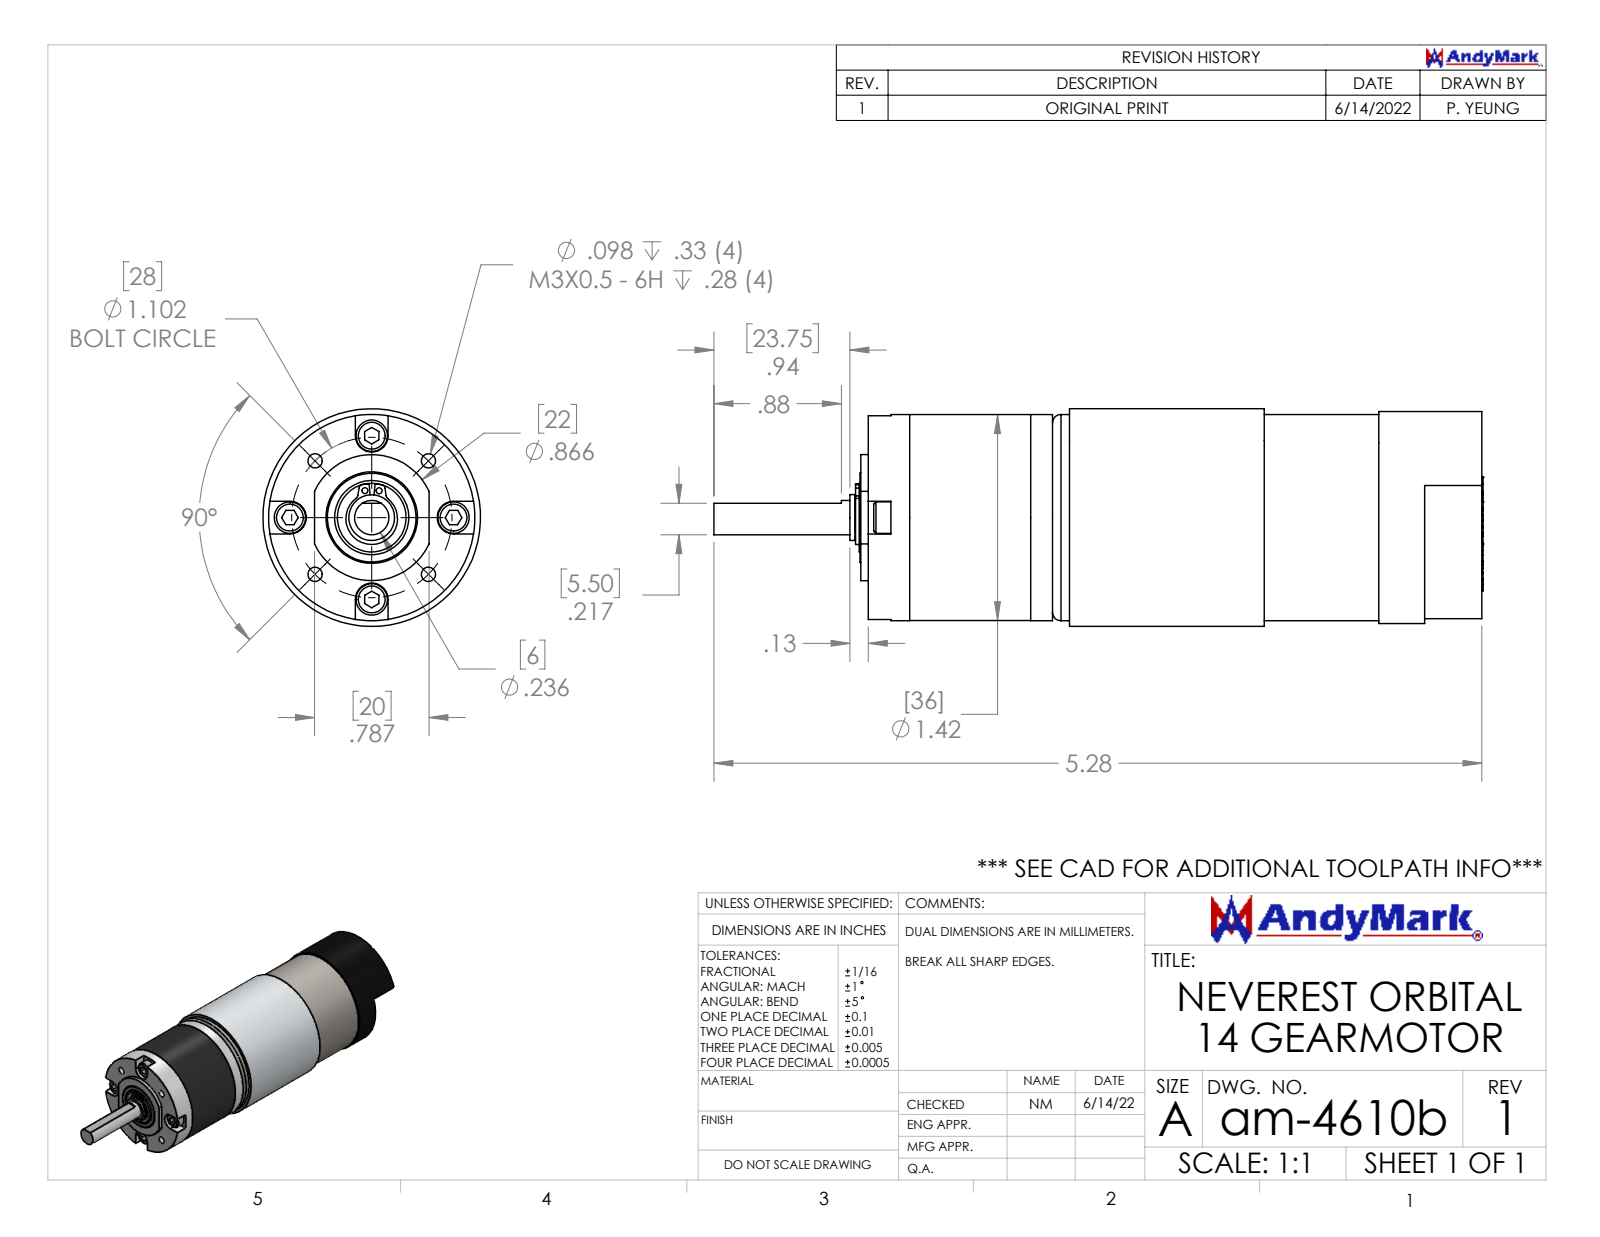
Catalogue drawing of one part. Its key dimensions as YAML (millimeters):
part_name: "am-4610b NeveRest Orbital 14 Gearmotor; am-3104 NeveRest Motor; am-4376 17T 0.5mod NeveRest Orbital Pinion; NR Orbital 2 Stage Gearbox (+5 more)"
step_written_by: "SolidWorks 2021 (AUTOMOTIVE_DESIGN)"
units: millimeters
bodies: {solids: 25, faces: 679, planar: 270, cylindrical: 199, other: 210}
overall_size: [134.3, 38, 38]
volume: 111100
surface_area: 23170
round_holes:
  - {diameter: 2.5, count: 10}
  - {diameter: 3.2, count: 4}
  - {diameter: 3.2, count: 3}
  - {diameter: 1, count: 2}
  - {diameter: 7.4, count: 1}
  - {diameter: 8, count: 1}
  - {diameter: 11, count: 1}
  - {diameter: 13, count: 1}
  - {diameter: 13, count: 1}
  - {diameter: 16, count: 1}
round_bosses_or_shafts:
  - {diameter: 5.5, count: 4}
  - {diameter: 3, count: 4}
  - {diameter: 38, count: 1}
  - {diameter: 37, count: 1}
  - {diameter: 36, count: 1}
  - {diameter: 35.9, count: 1}
  - {diameter: 12, count: 1}
  - {diameter: 6, count: 1}
partial_cylinders:
  - {radius: 1.6, count: 34}
  - {radius: 0.7, count: 4}
  - {radius: 2.8, count: 4}
  - {radius: 3.5, count: 1}
  - {radius: 4.5, count: 1}
  - {radius: 4.6, count: 1}
  - {radius: 11, count: 1}
face_to_face_distances: [75, 107.2, 32.2, 10, 5, 65, 97.2, 108.5, 98.5, 33.5]
hole_center_spacings: [10.8, 26.1, 10.4, 14, 18.8, 19.8, 14.3, 24.8]
